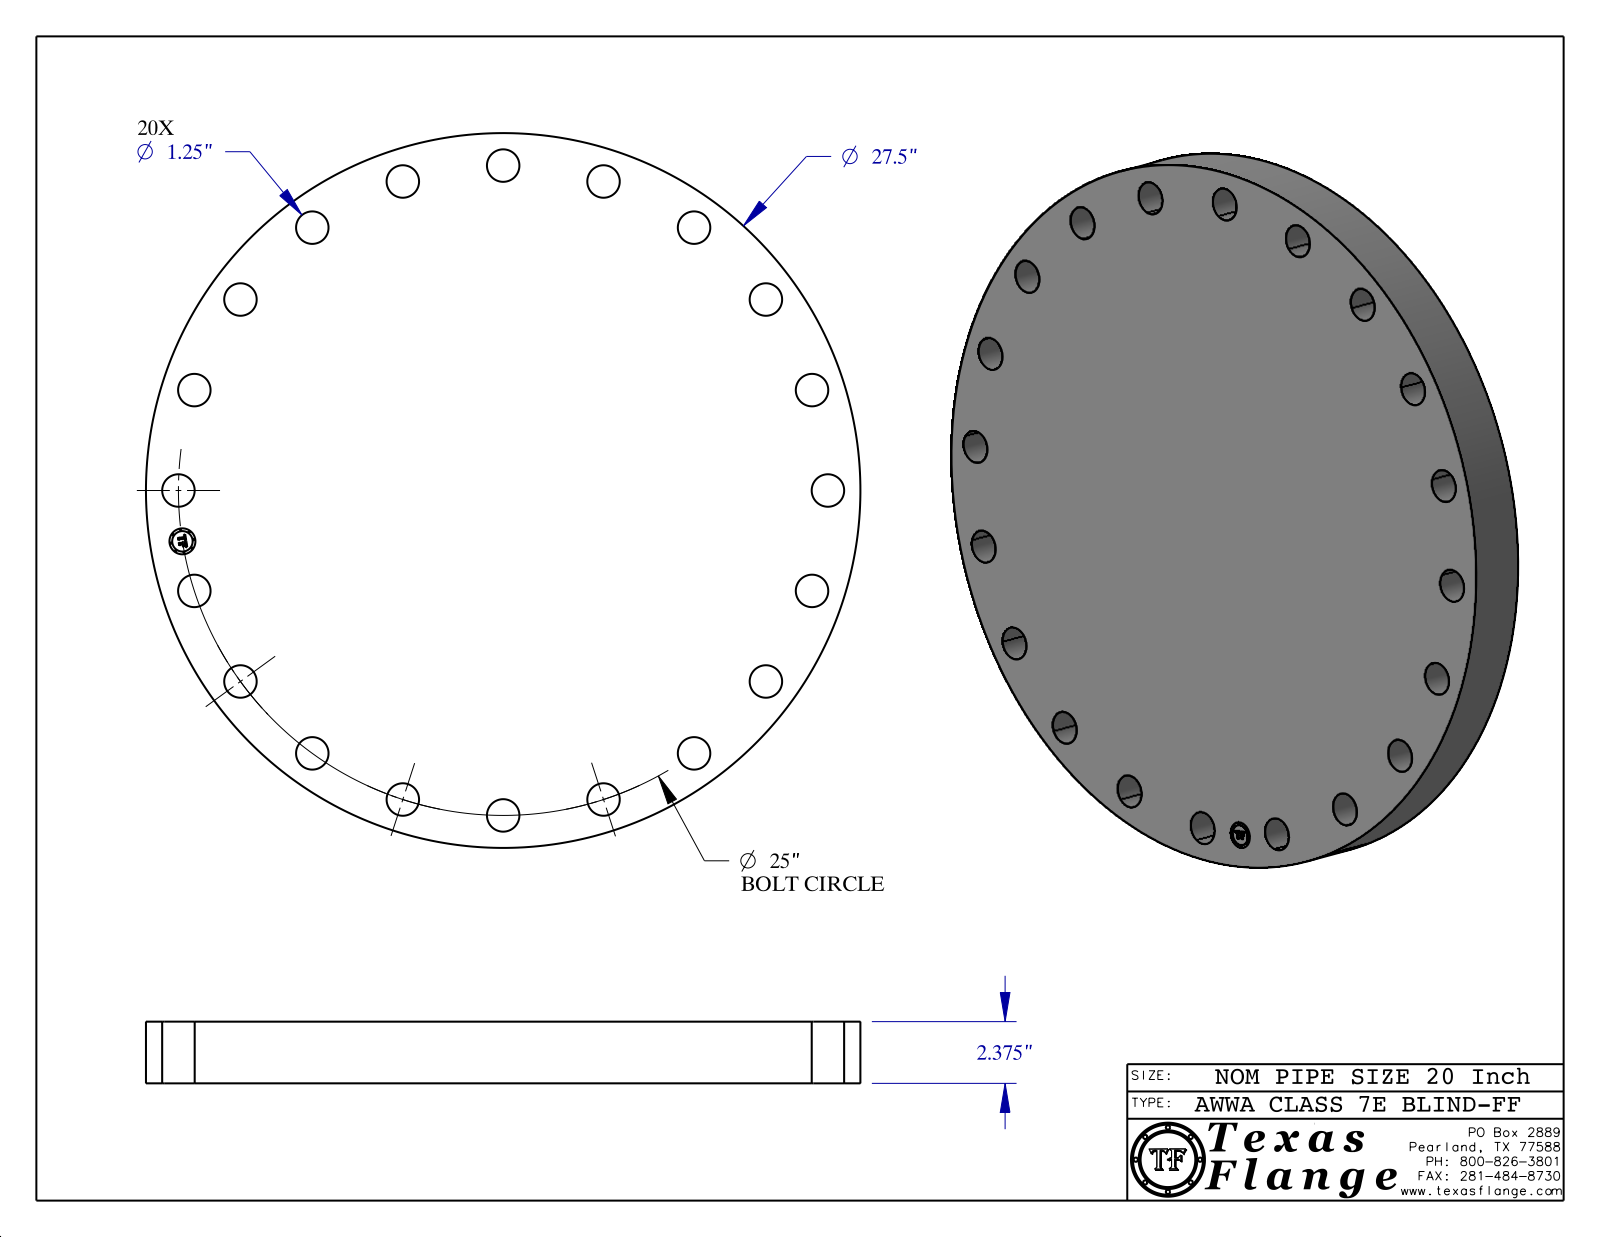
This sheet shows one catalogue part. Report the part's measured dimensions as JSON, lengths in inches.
{"part_name": "AWWA Class 7E-BLIND-FF", "step_written_by": "CATIA V5 STEP AP214 (AUTOMOTIVE_DESIGN)", "units": "inches", "bodies": {"solids": 1, "faces": 429, "planar": 367, "cylindrical": 62, "other": 0}, "overall_size": [27.5, 27.5, 2.375], "volume_in3": 1352, "surface_area_in2": 1531, "round_holes": [[1.25, 20], [1, 1]], "round_bosses_or_shafts": [[0.061, 8], [27.5, 1], [0.788, 1]], "face_to_face_distances": [2.375, 0.015, 2.36, 0.019, 0.298, 0.293, 0.054, 0.194, 0.248, 0.044], "hole_center_spacings": [14.694, 17.678, 20.225, 23.776, 24.692, 11.35, 22.275, 3.911]}
